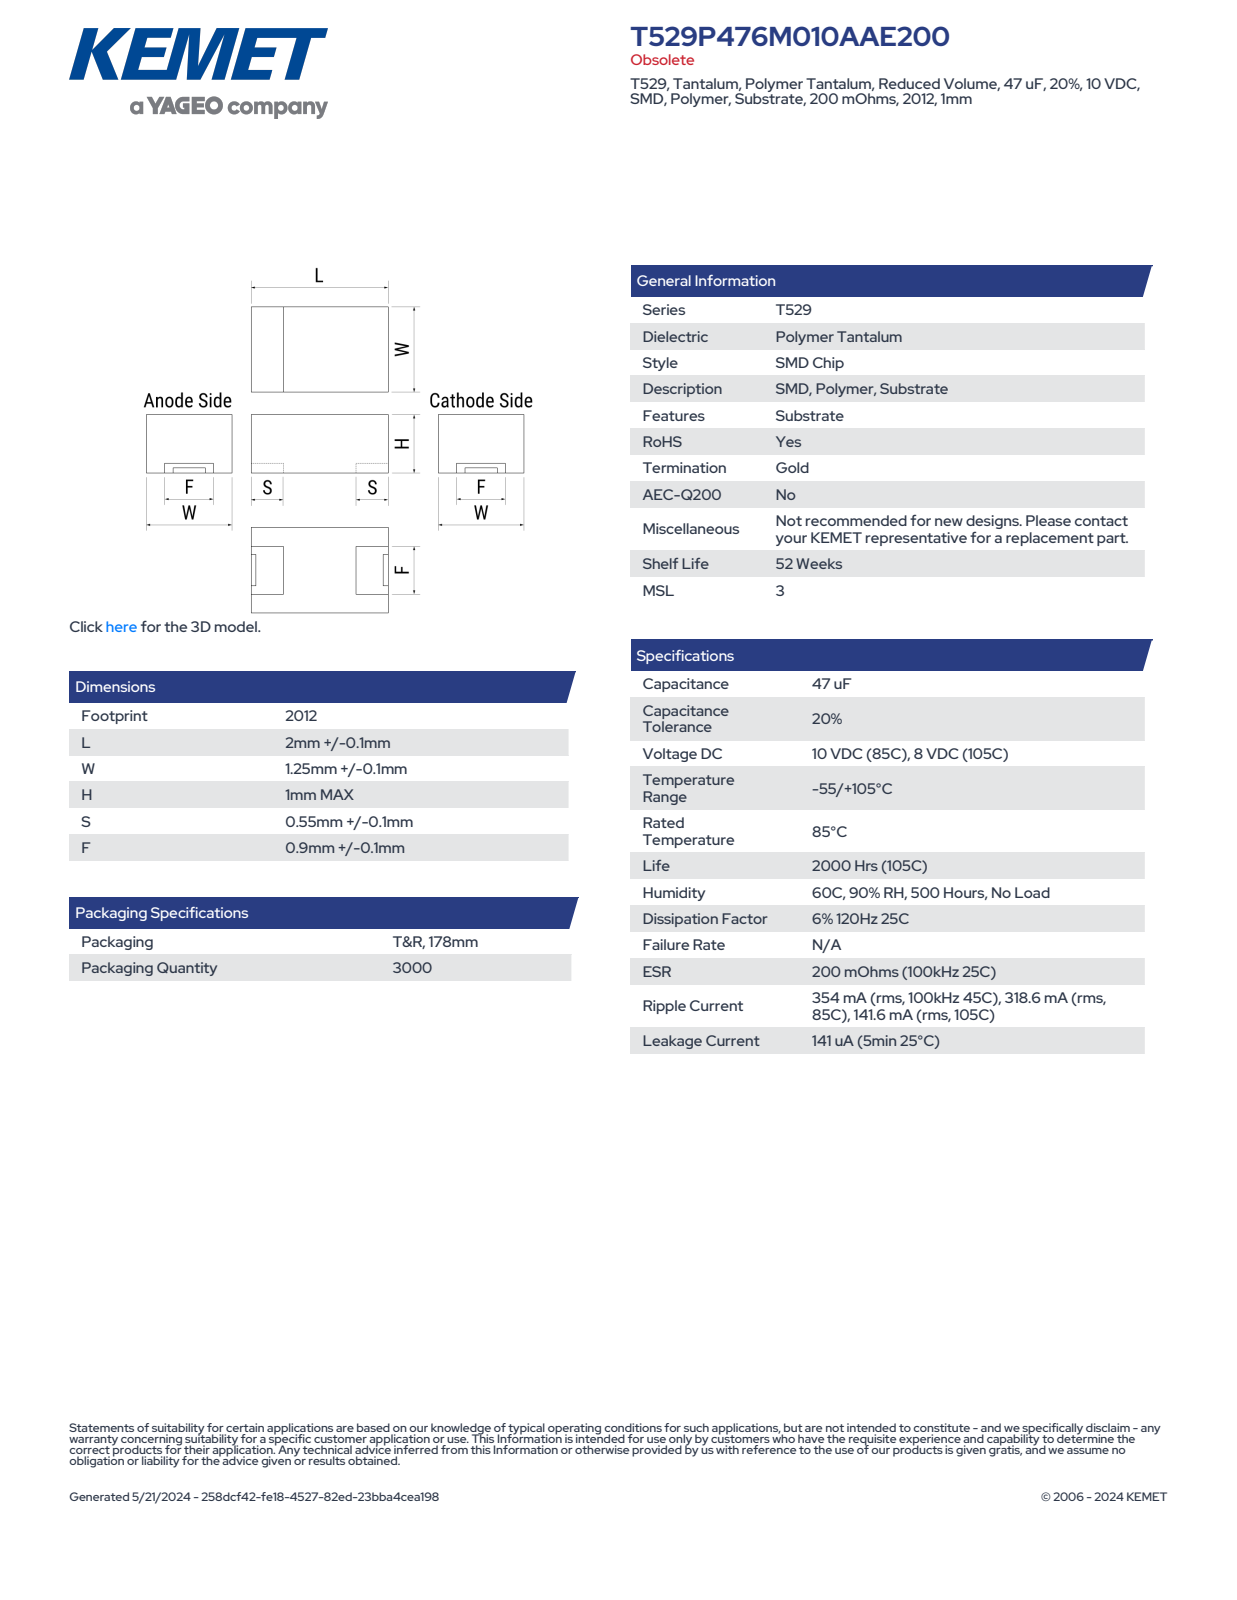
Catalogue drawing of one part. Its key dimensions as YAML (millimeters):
part_name: "T529_P-Case; Ta_SMT_P-Case_Anode+; CTSss2012P_L2W1.25H1S0.55F0.9; Ta_SMT_P-Case_SubstrateBoard (+1 more)"
step_written_by: "SolidWorks 2014 (AUTOMOTIVE_DESIGN)"
units: millimeters
bodies: {solids: 7, faces: 127, planar: 113, cylindrical: 10, other: 4}
overall_size: [2.1, 1.35, 1]
volume: 3
surface_area: 21
face_to_face_distances: [0.9, 1, 1.35, 2.1, 0.95, 0.85, 0.94, 1.12, 1.95, 1.4]
